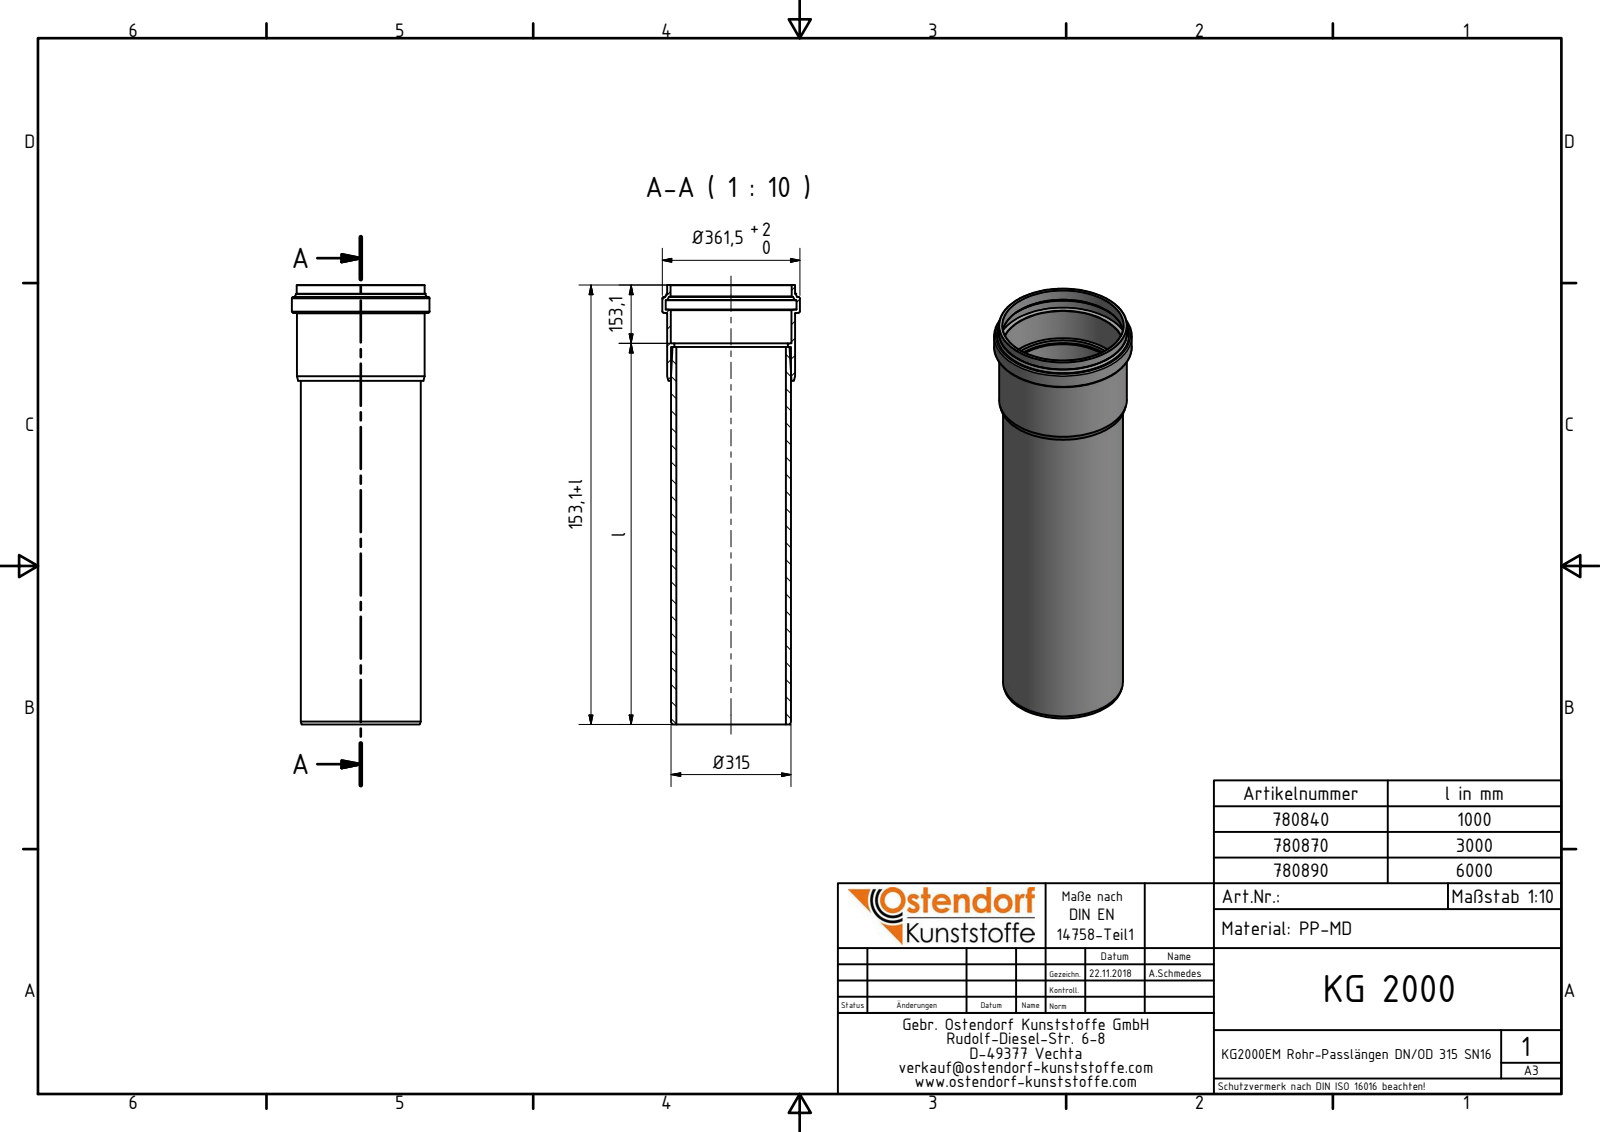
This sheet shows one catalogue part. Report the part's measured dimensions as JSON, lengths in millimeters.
{"part_name": "780870 KG2000EM Rohr-Passlängen DN_OD 315x3000 Teil1 SN16; 780870 KG2000EM Rohr-Passlängen DN_OD 315x3000 Teil2 SN16; 780870 KG2000EM Rohr-Passlängen DN_OD 315x3000 SN16 Zusammenbau", "step_written_by": "Autodesk Inventor 2016 (AUTOMOTIVE_DESIGN)", "units": "millimeters", "bodies": {"solids": 2, "faces": 40, "planar": 6, "cylindrical": 9, "other": 25}, "overall_size": [3153.1, 361.5, 361.5], "volume_mm3": 41370000, "surface_area_mm2": 6274000, "round_holes": [[287.8, 1], [298, 1], [317.3, 1], [317.7, 1], [343.3, 1]], "round_bosses_or_shafts": [[361.5, 1], [335.9, 1], [335.5, 1], [315, 1]], "face_to_face_distances": [2990.9, 3000, 9.1, 3153.1, 162.2, 153.1, 2901.9, 89, 98.1, 251.2]}
